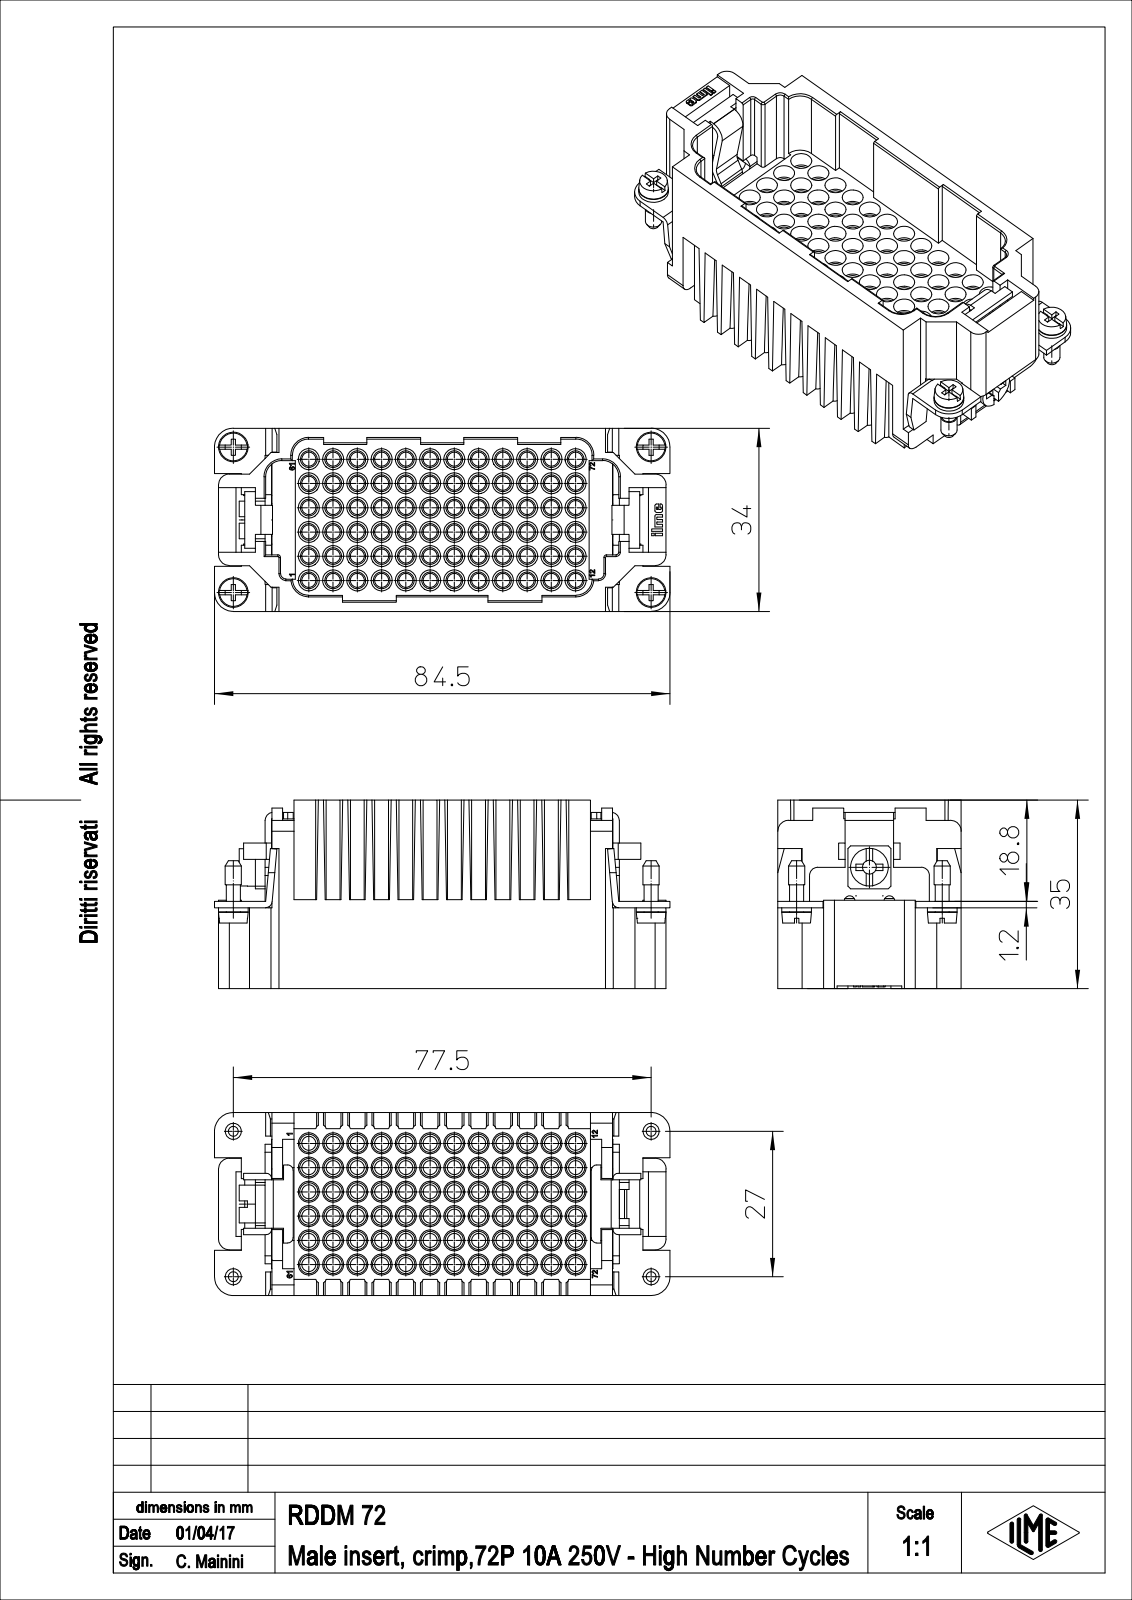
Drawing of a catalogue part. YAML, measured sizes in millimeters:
part_name: "RDDM_72"
step_written_by: "PTC Creo Elements/Direct Modeling 19.0E 27-Jun-2016 (C) Parametric Technology GmbH (AUTOMOTIVE_DESIGN)"
units: millimeters
bodies: {solids: 1, faces: 1998, planar: 831, cylindrical: 914, other: 253}
overall_size: [84.5, 35, 34]
volume: 33575
surface_area: 38034
round_holes:
  - {diameter: 2.6, count: 72}
  - {diameter: 3.1, count: 72}
  - {diameter: 3.4, count: 72}
  - {diameter: 3.9, count: 72}
  - {diameter: 2.58, count: 1}
  - {diameter: 3, count: 1}
round_bosses_or_shafts:
  - {diameter: 5.5, count: 4}
  - {diameter: 3, count: 4}
  - {diameter: 2.6, count: 4}
  - {diameter: 7, count: 1}
  - {diameter: 6, count: 1}
partial_cylinders:
  - {radius: 1, count: 36}
  - {radius: 0.3, count: 13}
  - {radius: 2, count: 8}
  - {radius: 3, count: 6}
  - {radius: 0.29, count: 5}
  - {radius: 0.21, count: 4}
  - {radius: 1.2, count: 4}
  - {radius: 1.5, count: 4}
face_to_face_distances: [3, 4.5, 31, 2, 9, 18, 34, 13.5, 22.5, 1]
hole_center_spacings: [10.06, 14.23, 16.22, 18.55, 4.5, 20.12, 22.5, 6.36]
